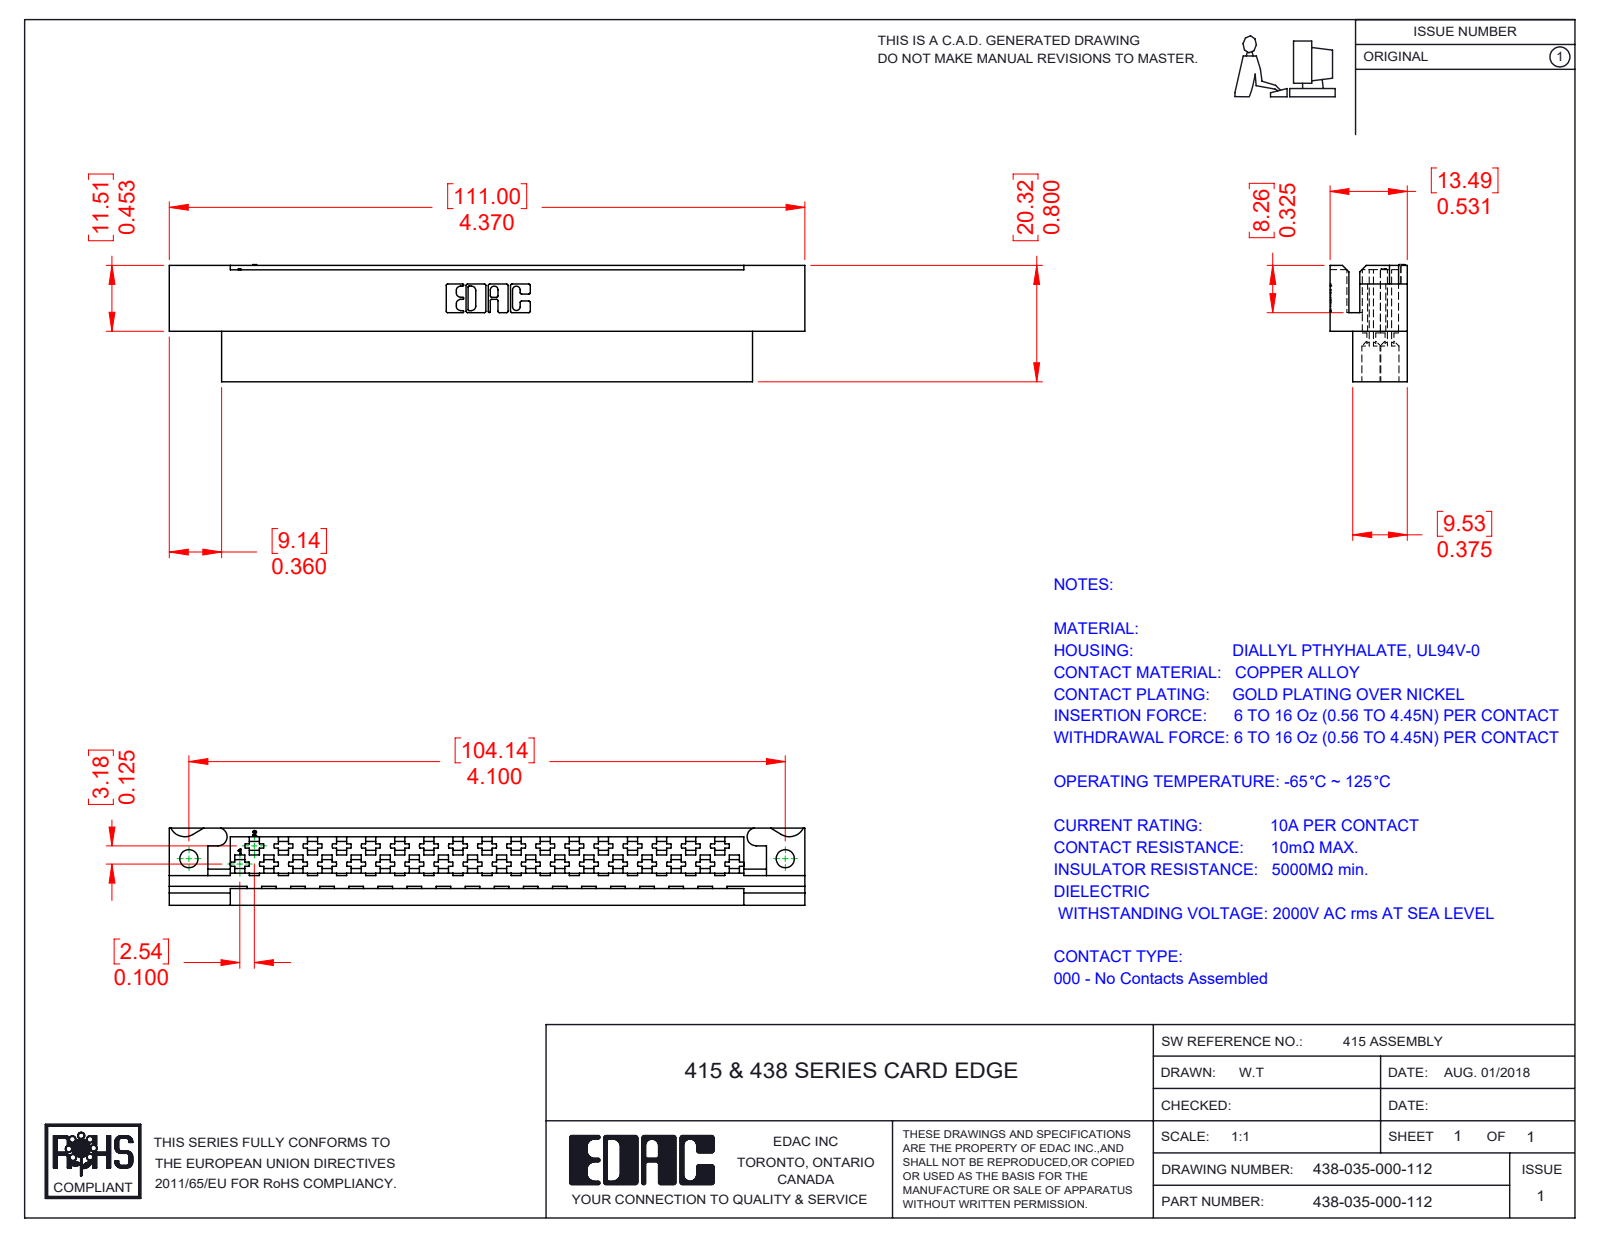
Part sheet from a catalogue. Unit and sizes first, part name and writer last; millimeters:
Units: millimetres
Overall size (bounding box): 111 × 20.45 × 13.49
Round holes (diameter × count): ⌀3.3 ×35, ⌀3.17 ×1, ⌀3.18 ×1
Partial cylindrical surfaces — rounded edges, fillets, slot ends (radius × count): R0.25 ×22, R0.17 ×6, R0.8 ×6, R0.67 ×3, R1.59 ×2, R2.7 ×2
Main face-to-face distances: 13.49, 9.53, 3.96, 3.18, 1.23, 3.17, 1.2, 0.74, 1.94, 4.38
Hole centre spacings: 5.08, 10.16, 4.06, 8.25, 15.24, 13.09, 18.06, 20.32
Volume: 16 941 mm³ · Surface area: 16 777 mm²
Bodies: 1 solid, 1066 faces (819 planar, 120 cylindrical, 127 other)
Part name (STEP PRODUCT): 438-035-000-112; 438-210-001_438-210-035-112
STEP written by: SolidWorks 2016 (CONFIG_CONTROL_DESIGN)
